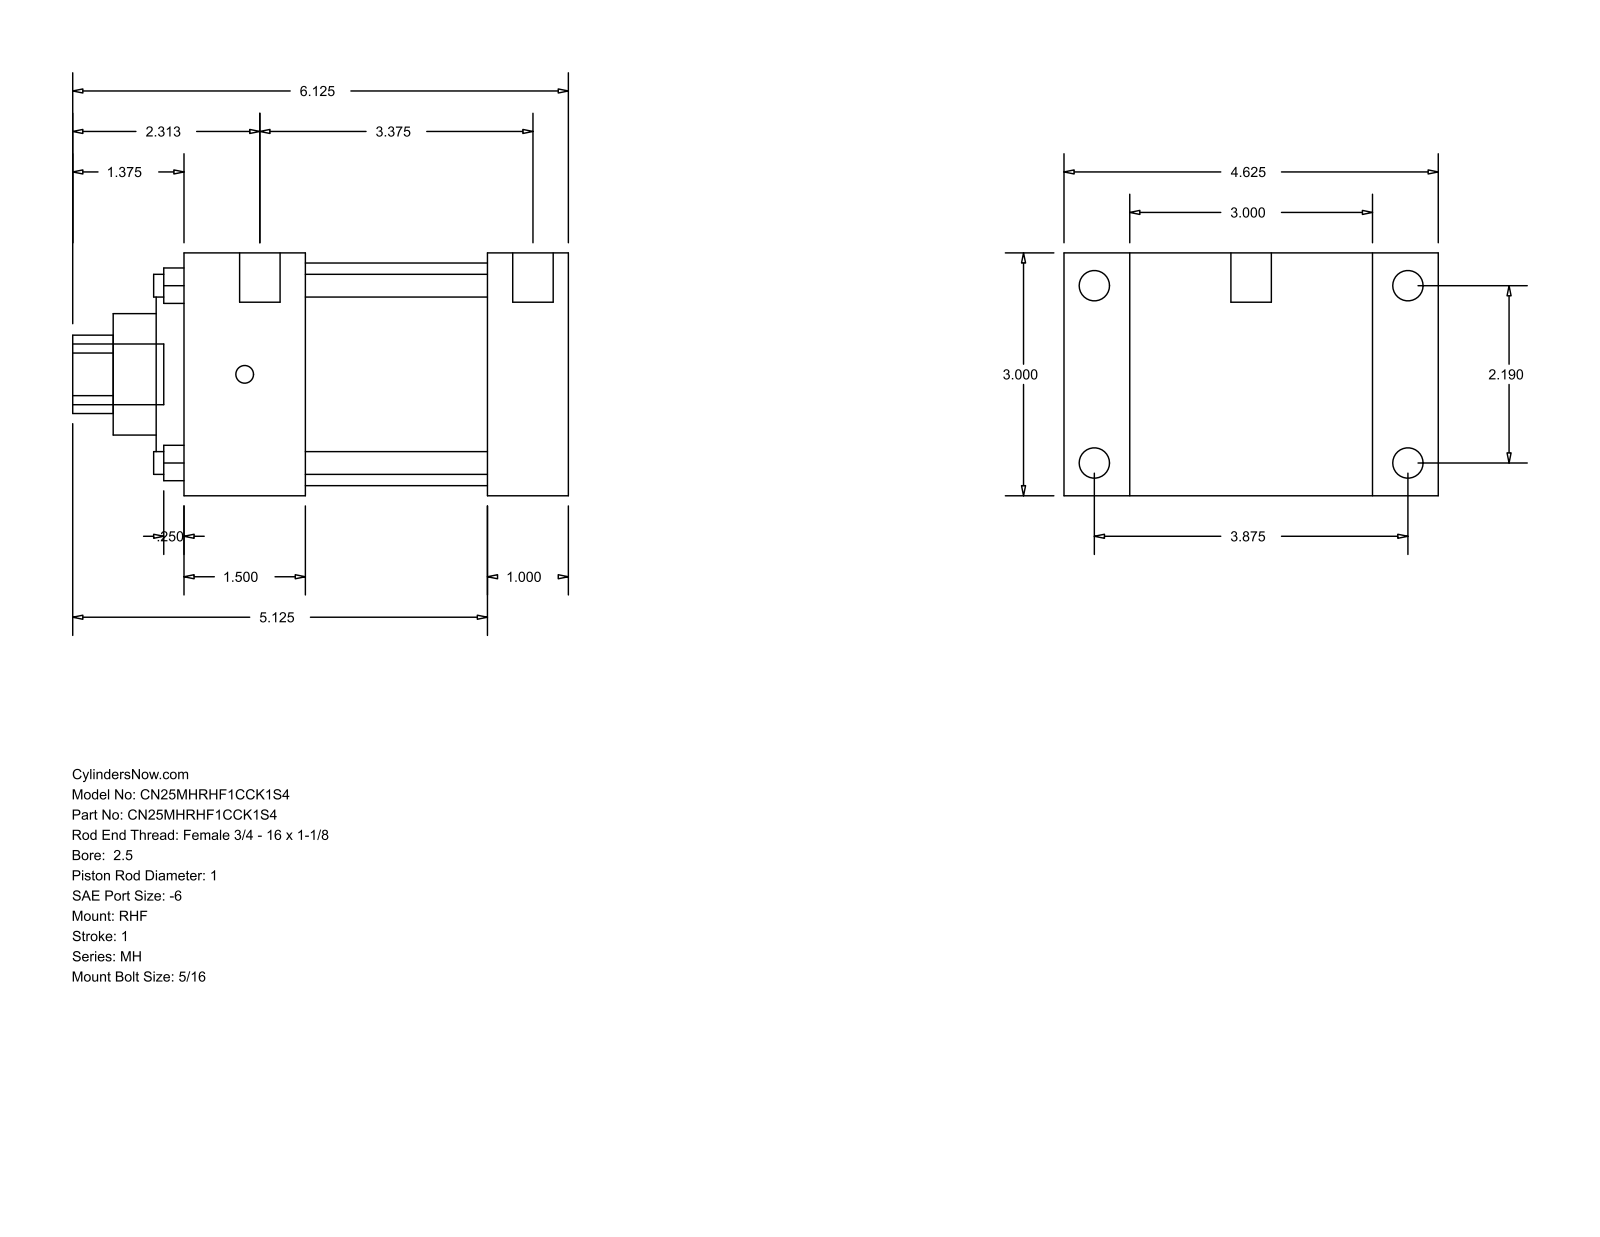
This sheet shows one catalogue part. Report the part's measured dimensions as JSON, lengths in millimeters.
{"part_name": "MH_RHF__0250_1", "step_written_by": "GSSL Pune (CONFIG_CONTROL_DESIGN)", "units": "millimeters", "bodies": {"solids": 0, "faces": 90, "planar": 61, "cylindrical": 29, "other": 0}, "overall_size": [155.57, 117.47, 76.2], "round_holes": [[7.14, 4], [25.4, 1], [38.1, 1], [60.33, 1], [69.85, 1]], "round_bosses_or_shafts": [[9.53, 4], [5.56, 4], [12.7, 2], [19.05, 1]], "partial_cylinders_radius": [[12.29, 1]], "face_to_face_distances": [76.2, 25.39, 20.64, 96.84, 120.65, 117.48, 95.26, 38.11, 57.15, 82.54], "hole_center_spacings": [39.33, 55.62, 78.66]}
